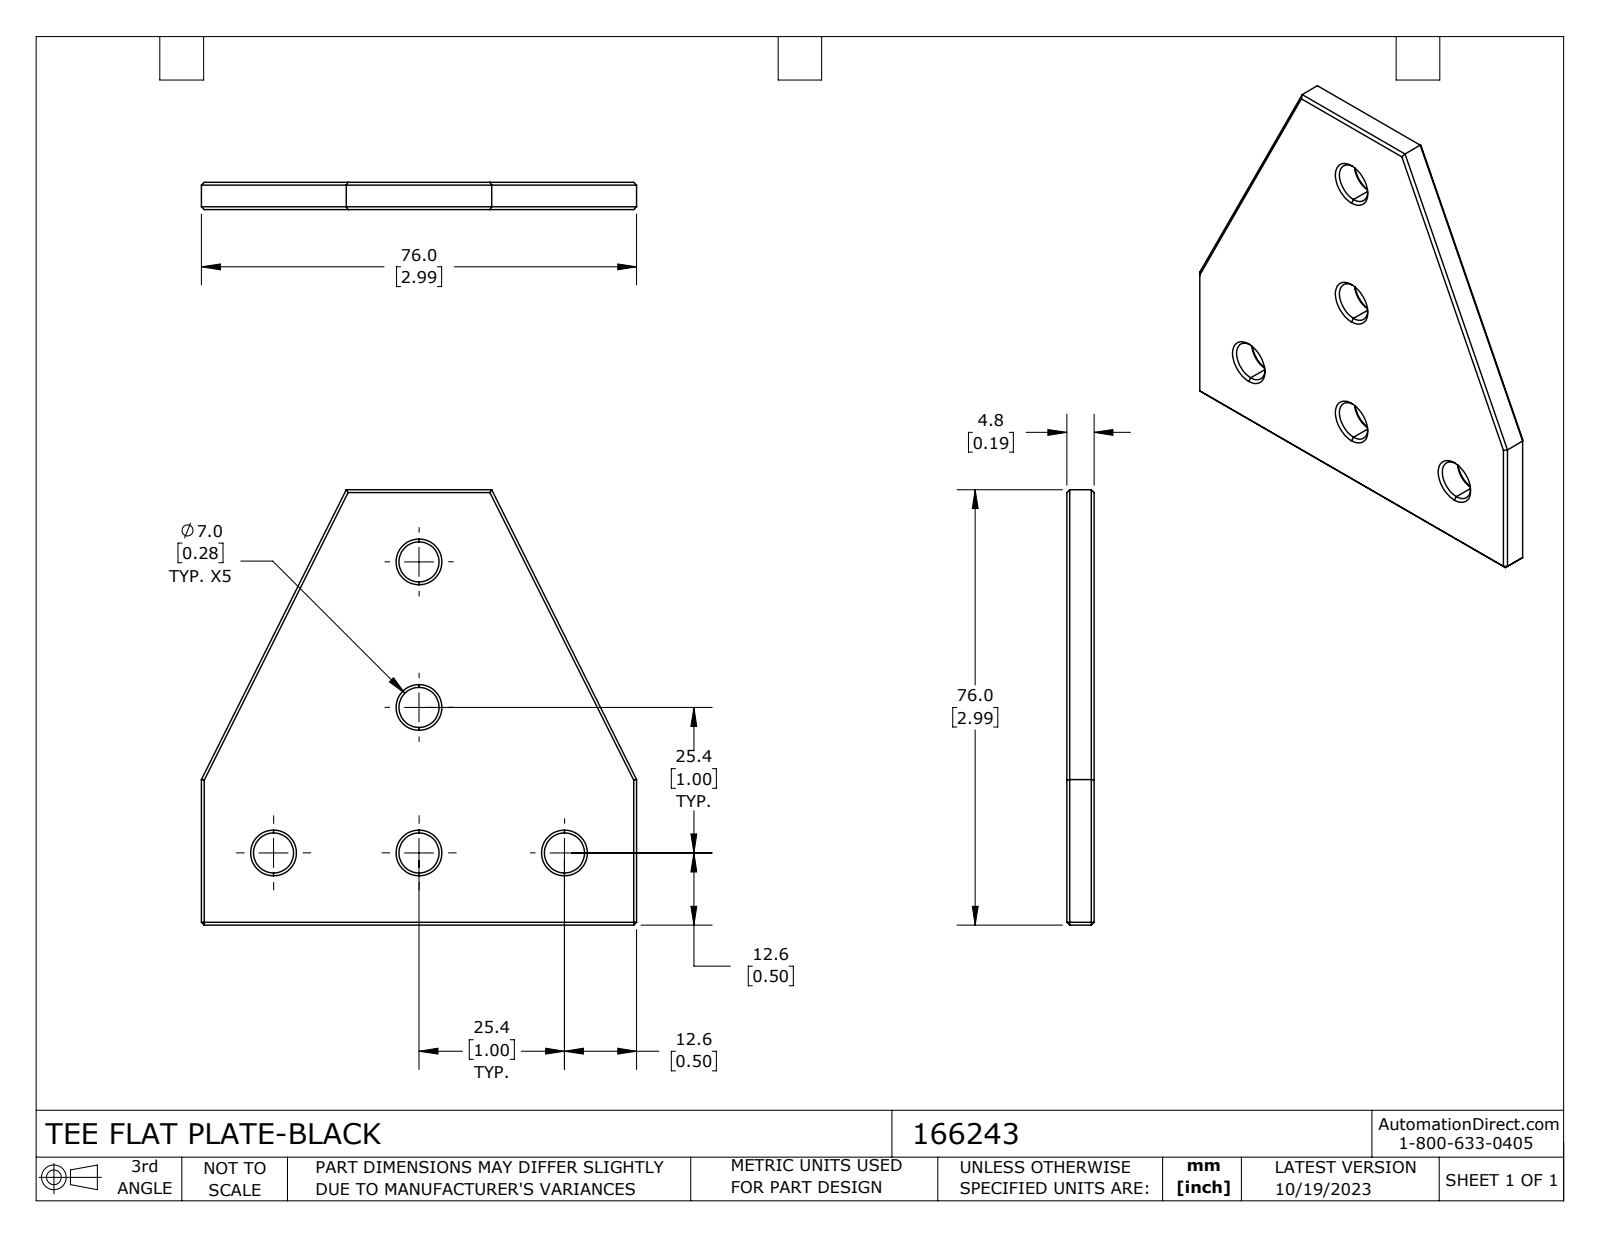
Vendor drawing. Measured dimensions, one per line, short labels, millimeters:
name: 166243
written by: SolidWorks 2023 (CONFIG_CONTROL_DESIGN)
unit: mm
bodies: 1 solid, 56 faces (26 planar, 10 cylindrical, 20 other)
size: 76 × 76 × 4.76
volume: 20 399 mm³; area: 10 174 mm²
holes: 5× ⌀7
face distances: 4.76, 76, 56.39
hole spacings: 25.4, 35.92, 50.8, 56.8
